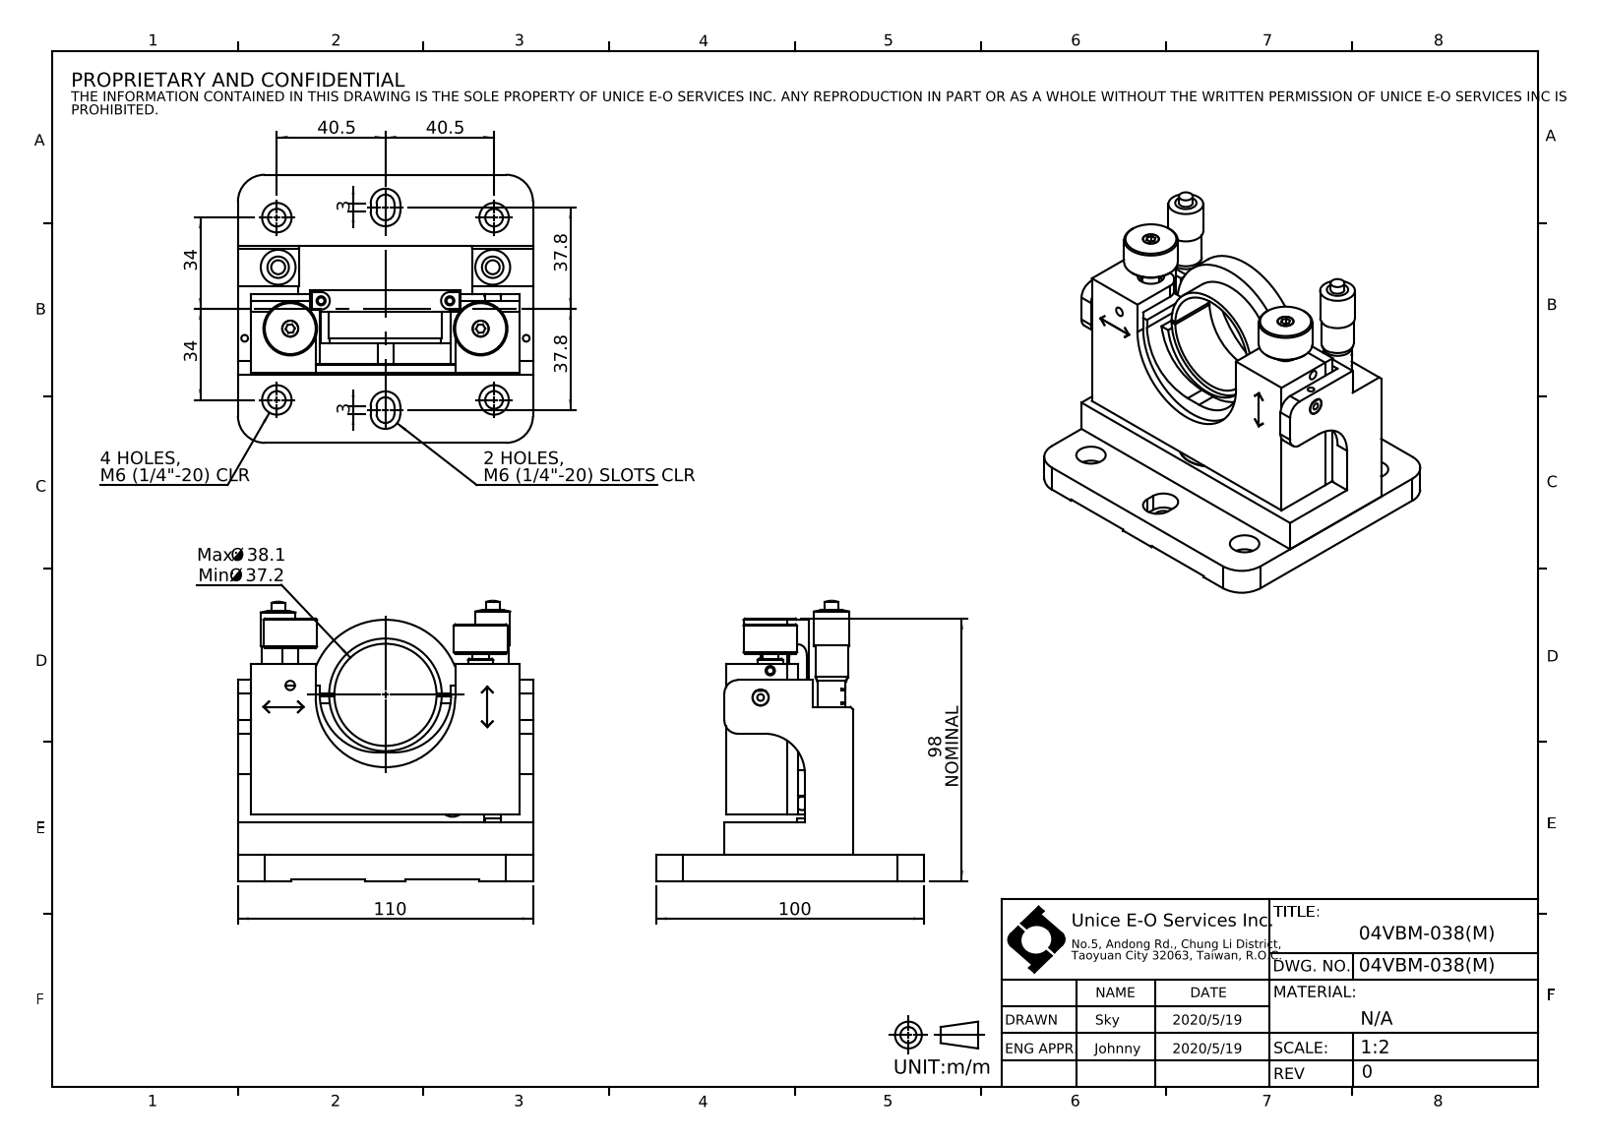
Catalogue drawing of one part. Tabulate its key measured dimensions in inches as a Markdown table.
| quantity | value |
| --- | --- |
| part name | 04VBM-038(M) |
| STEP written by | SolidWorks 2016 (CONFIG_CONTROL_DESIGN) |
| units | inches |
| bodies | 0 solids, 343 faces (167 planar, 137 cylindrical, 39 other) |
| overall size | 4.331 × 4.118 × 3.937 |
| round holes (diameter × count) | 0.098 × 5, 0.26 × 5, 0.433 × 4, 0.256 × 3, 0.079 × 2, 0.134 × 2, 0.138 × 2, 0.276 × 2, 0.197 × 1, 0.236 × 1, 0.394 × 1, 1.5 × 1 |
| round bosses / shafts (diameter × count) | 0.787 × 2, 0.512 × 2, 0.472 × 2, 0.413 × 2, 0.374 × 2, 0.205 × 2, 0.063 × 2, 1.654 × 1 |
| partial cylindrical surfaces (radius × count) | 0.039 × 4, 0.13 × 4, 0.217 × 4, 0.394 × 4, 0.128 × 2, 0.197 × 2, 0.236 × 2, 0.846 × 2 |
| main face-to-face distances | 0.02, 0.374, 0.394, 0.197, 0.472, 1.161, 4.134, 1.87, 0.709, 0.965 |
| hole center spacings | 0.965, 1.339, 3.459, 3.189, 0.636, 0.641, 0.763, 1.021 |
